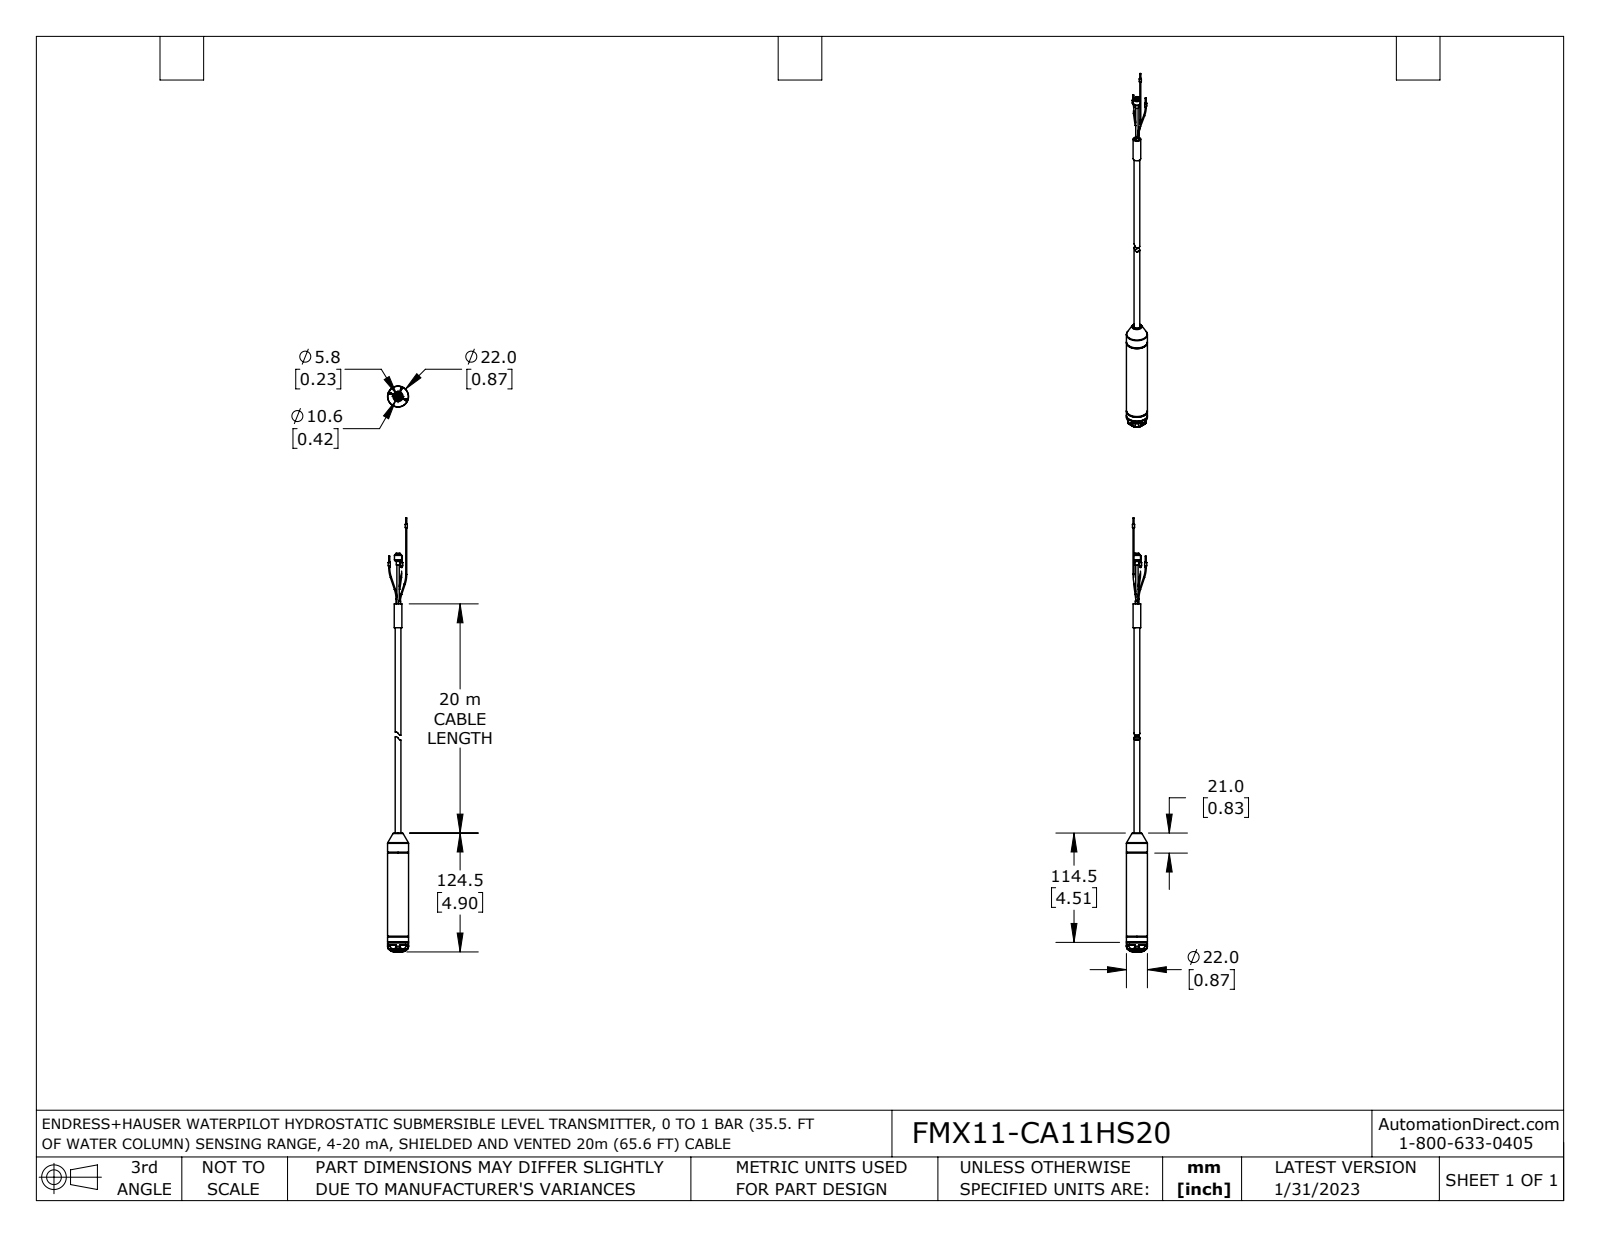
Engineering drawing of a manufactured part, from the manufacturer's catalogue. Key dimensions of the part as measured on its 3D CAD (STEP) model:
Part name (STEP PRODUCT): 3D_FMX11 CUT 1 fxt
STEP written by: SolidWorks 2021 (AUTOMOTIVE_DESIGN)
Units: inches
Bodies: 5 solids, 530 faces (136 planar, 160 cylindrical, 234 other)
Overall size (bounding box): 17.894 × 0.866 × 0.866
Volume: 3.056 in³ · Surface area: 28.22 in²
Round holes (diameter × count): ⌀0.071 ×3, ⌀0.051 ×1, ⌀0.063 ×1, ⌀0.067 ×1, ⌀0.094 ×1, ⌀0.234 ×1, ⌀0.24 ×1, ⌀0.317 ×1, ⌀0.358 ×1, ⌀0.522 ×1, ⌀0.571 ×1, ⌀0.657 ×1
Round bosses / shafts (diameter × count): ⌀0.039 ×9, ⌀0.087 ×3, ⌀0.043 ×3, ⌀0.866 ×1, ⌀0.813 ×1, ⌀0.606 ×1, ⌀0.315 ×1, ⌀0.297 ×1
Partial cylindrical surfaces — rounded edges, fillets, slot ends (radius × count): R0.01 ×8, R0.004 ×4, R0.02 ×4, R0.079 ×4, R0.157 ×4, R0.067 ×2, R0.092 ×2, R0.128 ×2
Main face-to-face distances: 0.039, 0.221, 0.507, 0.546, 0.285, 0.261, 0.02, 0.059, 0.305, 0.202
Hole centre spacings: 0.394, 0.071, 0.295, 0.366, 0.4, 0.465, 0.538, 0.557
